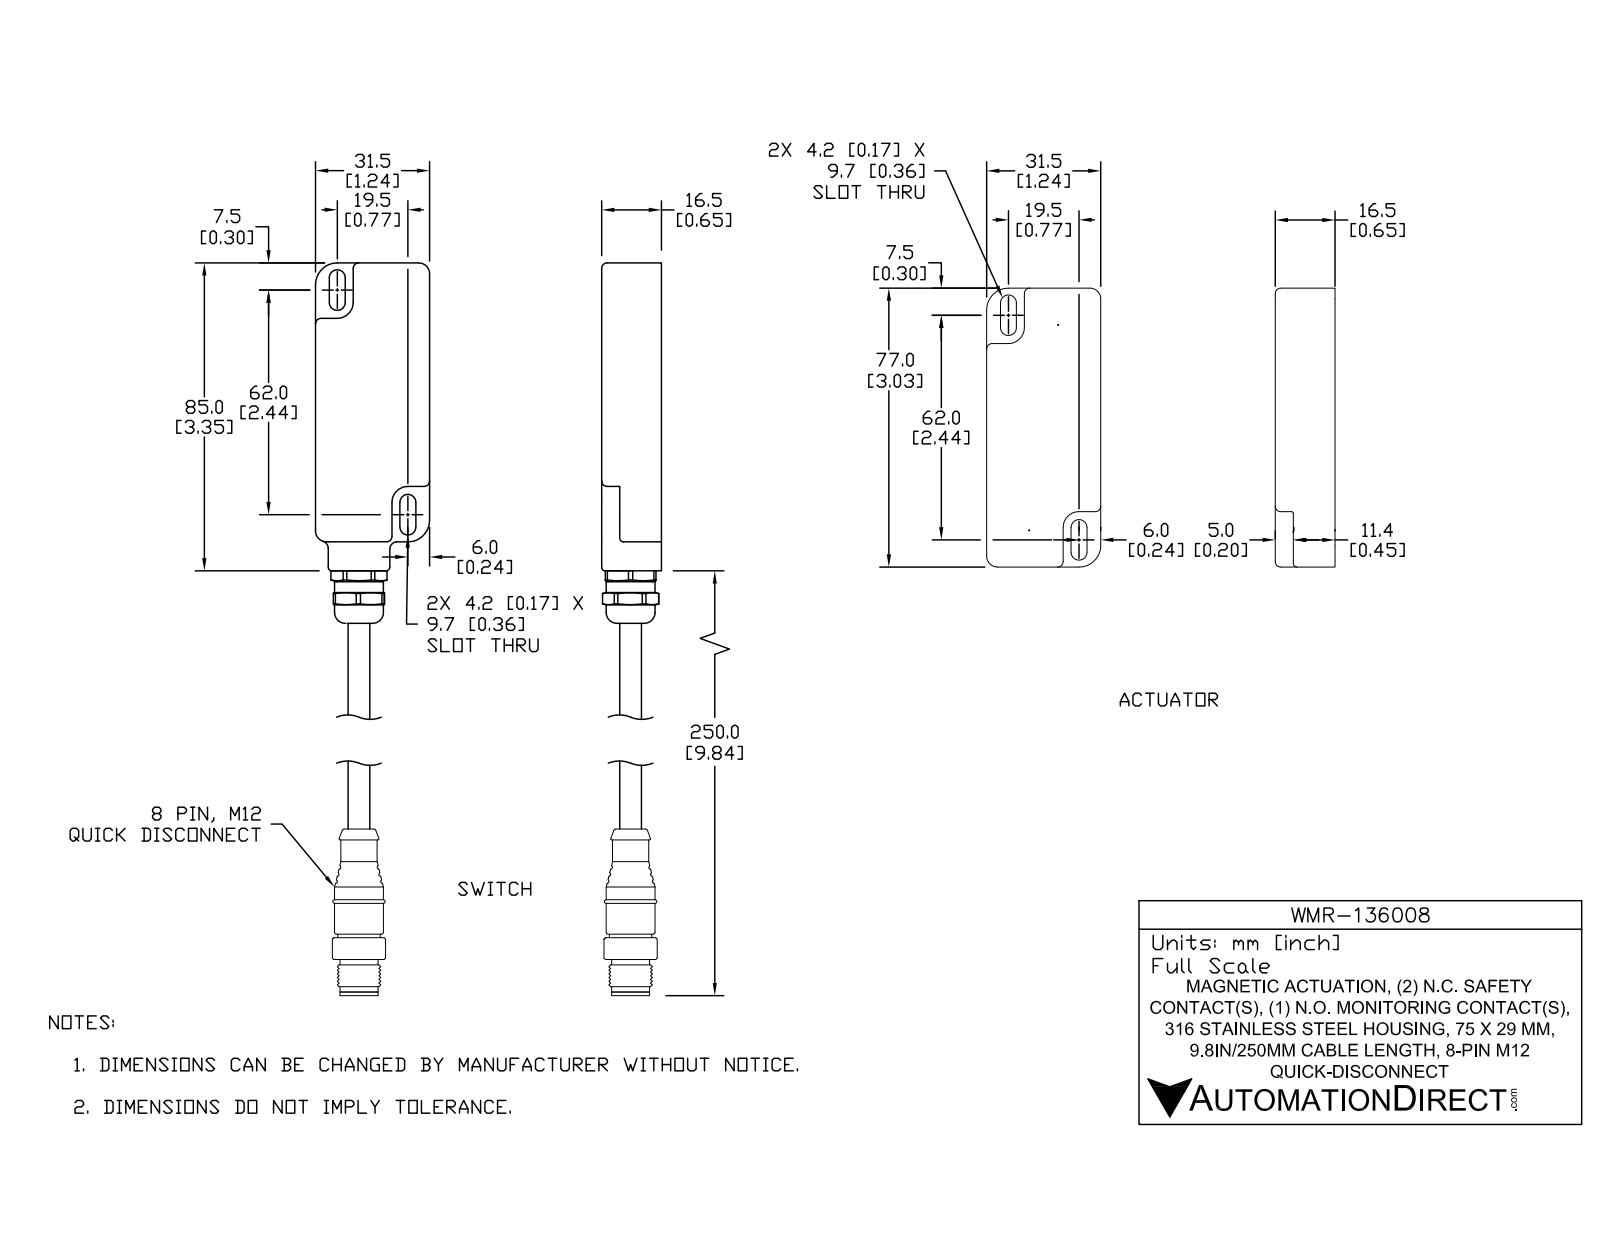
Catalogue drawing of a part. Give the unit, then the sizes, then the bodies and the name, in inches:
Units: inches
Overall size (bounding box): 13.189 × 2.52 × 0.65
Round holes (diameter × count): ⌀0.197 ×4, ⌀0.244 ×1, ⌀0.252 ×1, ⌀0.268 ×1, ⌀0.327 ×1, ⌀0.354 ×1, ⌀0.374 ×1, ⌀0.406 ×1, ⌀0.453 ×1, ⌀0.465 ×1, ⌀0.512 ×1
Round bosses / shafts (diameter × count): ⌀0.031 ×8, ⌀0.193 ×4, ⌀0.079 ×4, ⌀0.531 ×1, ⌀0.472 ×1, ⌀0.461 ×1, ⌀0.413 ×1, ⌀0.394 ×1
Partial cylindrical surfaces — rounded edges, fillets, slot ends (radius × count): R0.02 ×134, R0.059 ×24, R0.039 ×19, R0.012 ×12, R0.087 ×8, R0.224 ×6, R0.016 ×5, R0.118 ×4
Main face-to-face distances: 0.079, 1.28, 0.646, 0.571, 0.075, 0.567, 1.161, 0.579, 0.067, 0.583
Hole centre spacings: 2.254, 2.573, 0.965, 1.594
Volume: 2.784 in³ · Surface area: 69.78 in²
Bodies: 13 solids, 1146 faces (389 planar, 414 cylindrical, 343 other)
Part name (STEP PRODUCT): WMR-136008; WMR-136008_1; WMR-136008_2
STEP written by: SolidWorks 2017 (AUTOMOTIVE_DESIGN)
